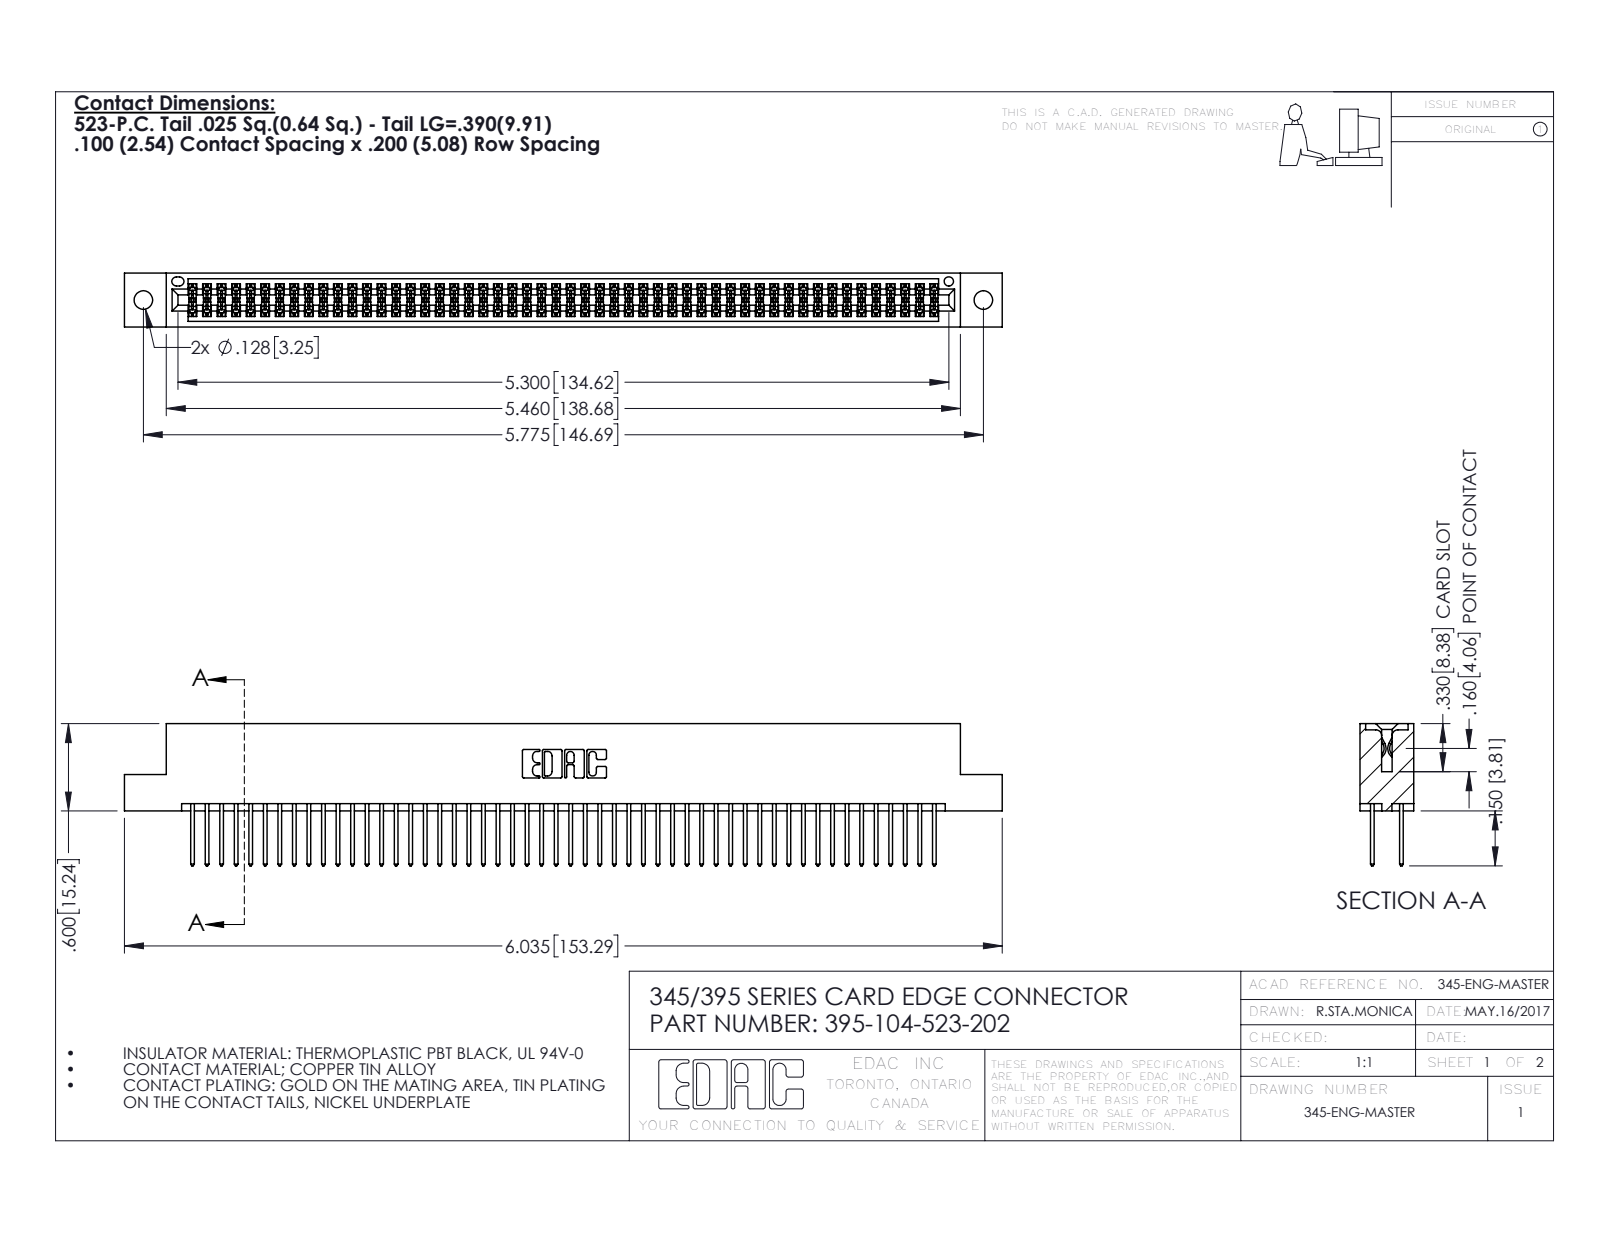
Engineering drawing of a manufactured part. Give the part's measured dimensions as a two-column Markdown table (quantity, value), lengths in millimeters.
| quantity | value |
| --- | --- |
| part name | 395-104-523-202; 345 Part_Flush Mounting Lugs - 0.128 Dia; 345-292-001_345-293-123 |
| STEP written by | SolidWorks 2016 (CONFIG_CONTROL_DESIGN) |
| units | millimeters |
| bodies | 105 solids, 5326 faces (3512 planar, 1814 cylindrical, 0 other) |
| overall size | 153.3 × 24.8 × 9.4 |
| volume | 15 200 mm³ |
| surface area | 23 280 mm² |
| round holes (diameter × count) | 3.3 × 2, 1.6 × 1 |
| partial cylindrical surfaces (radius × count) | 0.2 × 156, 0.3 × 104, 0.3 × 22, 0.2 × 6, 0.8 × 6, 0.7 × 3, 0.4 × 2, 0.5 × 2 |
| main face-to-face distances | 7.6, 1.8, 5.1, 2.5, 6.9, 0.6, 9.4, 5.7, 4.4, 3.8 |
| hole center spacings | 6.9, 140.7, 146.7 |
